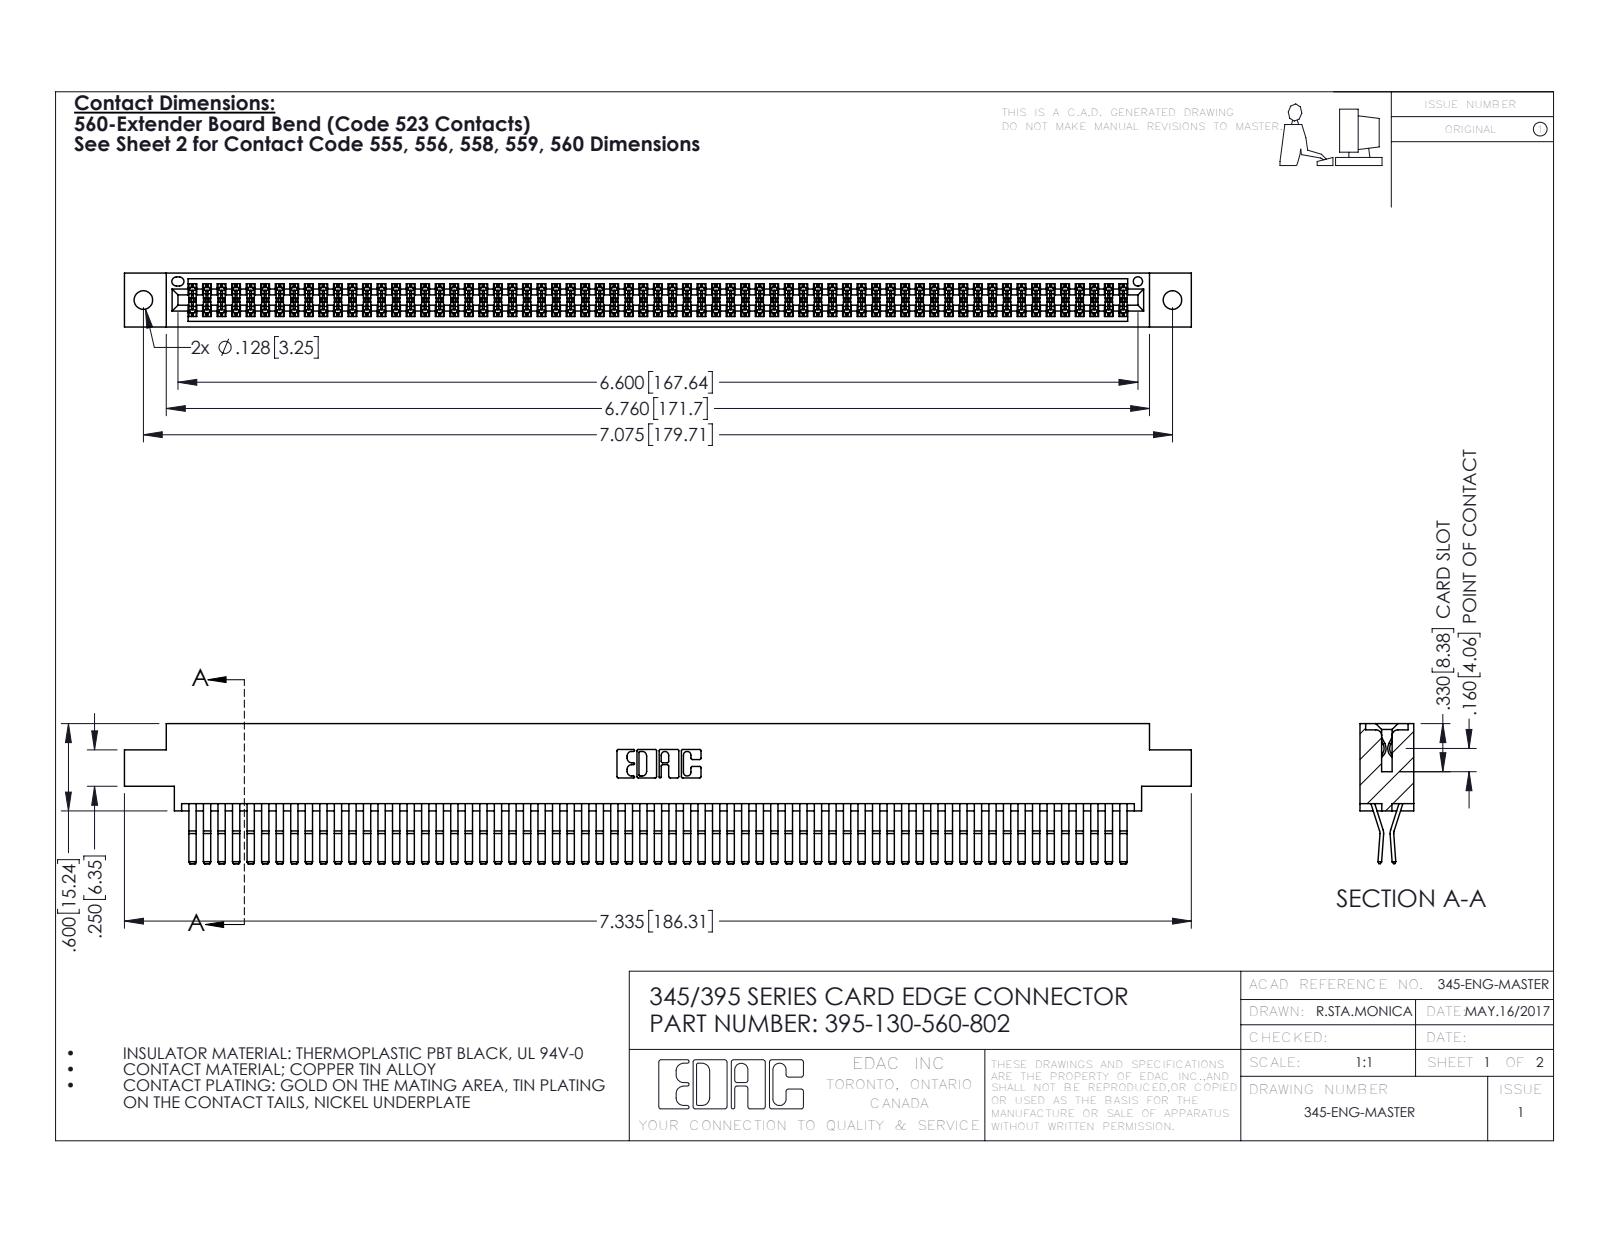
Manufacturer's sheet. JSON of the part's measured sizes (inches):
{"part_name": "345 Part_0.170 Offset - 0.128 Dia; 395-130-560-802; 345-292-001_560 Tail", "step_written_by": "SolidWorks 2016 (CONFIG_CONTROL_DESIGN)", "units": "inches", "bodies": {"solids": 131, "faces": 6890, "planar": 4374, "cylindrical": 2516, "other": 0}, "overall_size": [7.335, 0.962, 0.37], "volume_in3": 1.16, "surface_area_in2": 47.45, "round_holes": [[0.128, 2], [0.064, 1]], "partial_cylinders_radius": [[0.006, 196], [0.01, 22], [0.007, 6], [0.031, 6], [0.026, 3], [0.01, 2], [0.014, 2], [0.019, 2]], "face_to_face_distances": [0.025, 0.298, 0.072, 0.37, 0.2, 0.098, 0.272, 0.225, 0.175, 0.149], "hole_center_spacings": [0.27, 6.839, 7.075]}
